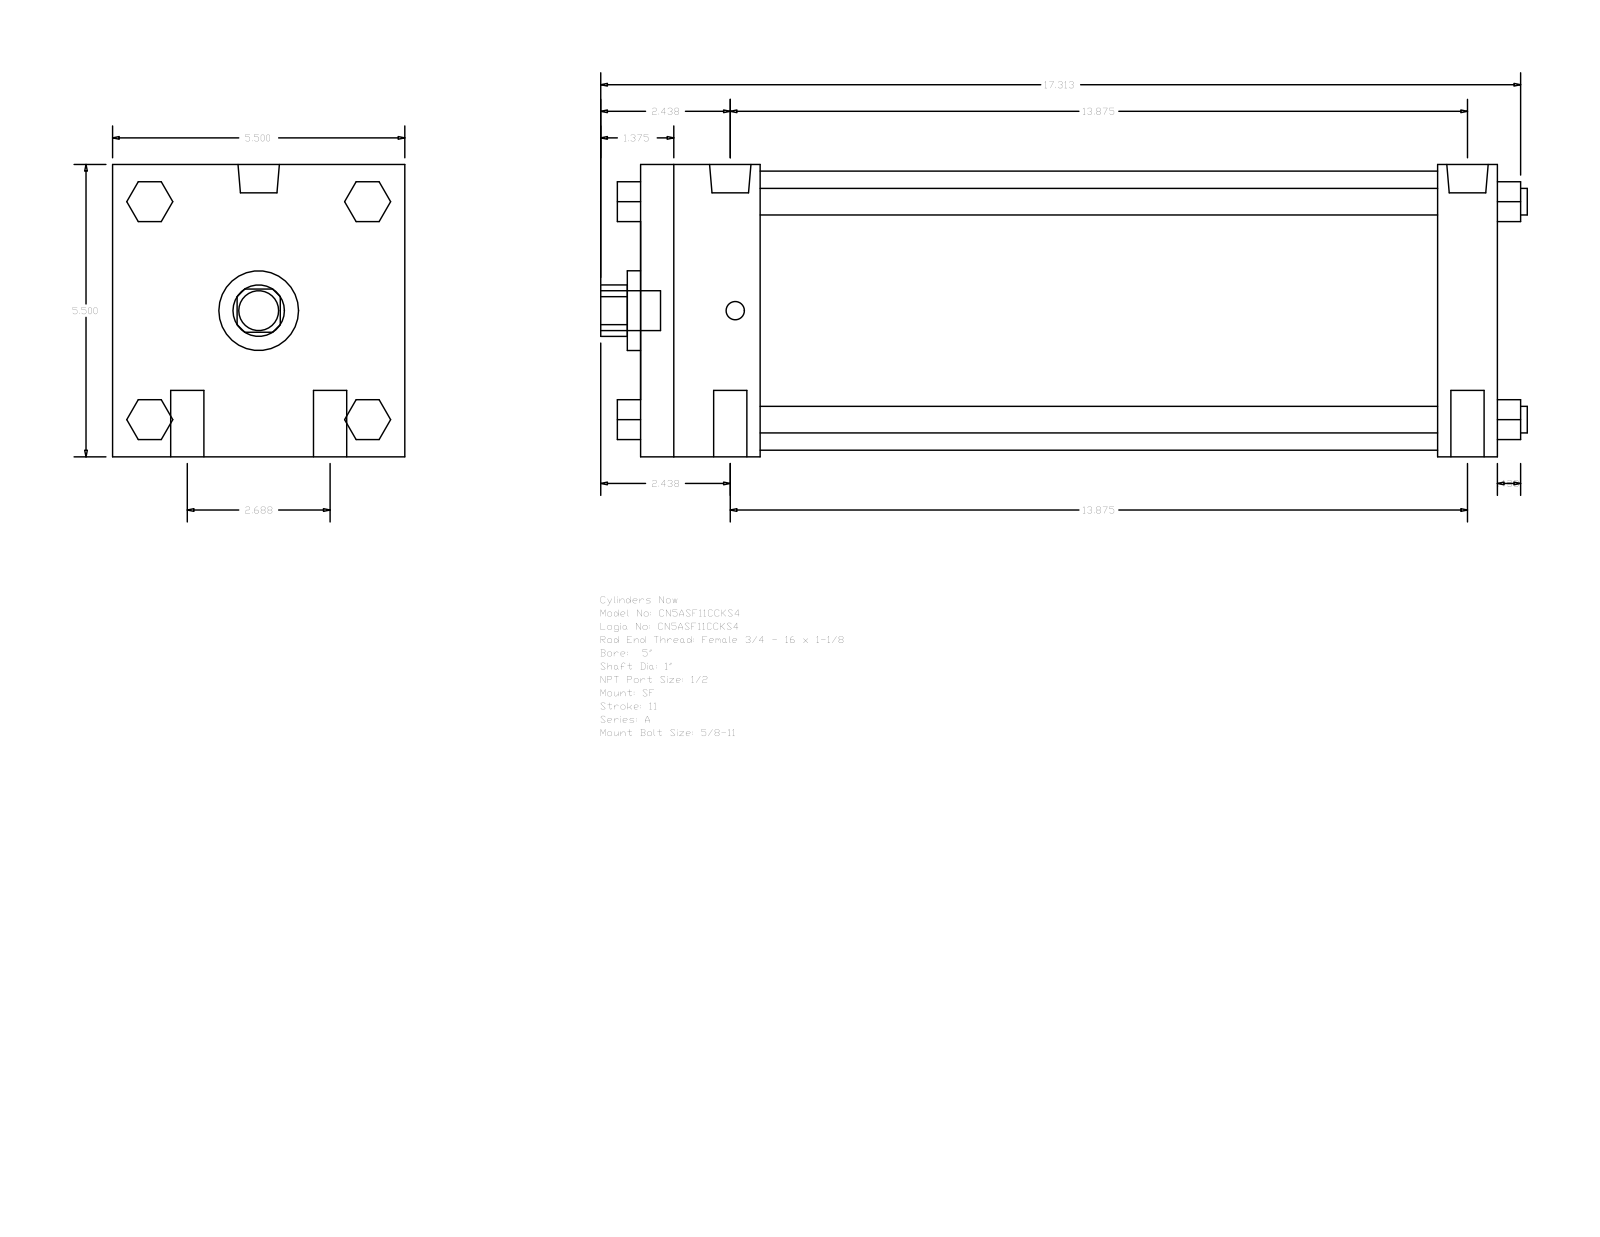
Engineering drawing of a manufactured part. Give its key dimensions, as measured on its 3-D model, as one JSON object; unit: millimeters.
{"part_name": "A_SF__0500_1", "step_written_by": "GSSL Pune (CONFIG_CONTROL_DESIGN)", "units": "millimeters", "bodies": {"solids": 0, "faces": 124, "planar": 94, "cylindrical": 30, "other": 0}, "overall_size": [442.91, 139.7, 139.7], "round_holes": [[25.4, 1], [38.1, 1], [133.35, 1]], "round_bosses_or_shafts": [[15.88, 4], [12.7, 4], [19.77, 2], [8.73, 2], [19.05, 1]], "partial_cylinders_radius": [[12.29, 1]], "face_to_face_distances": [139.7, 409.57, 28.57, 57.15, 381, 323.85, 352.42, 19.05, 52.07, 90.18]}
